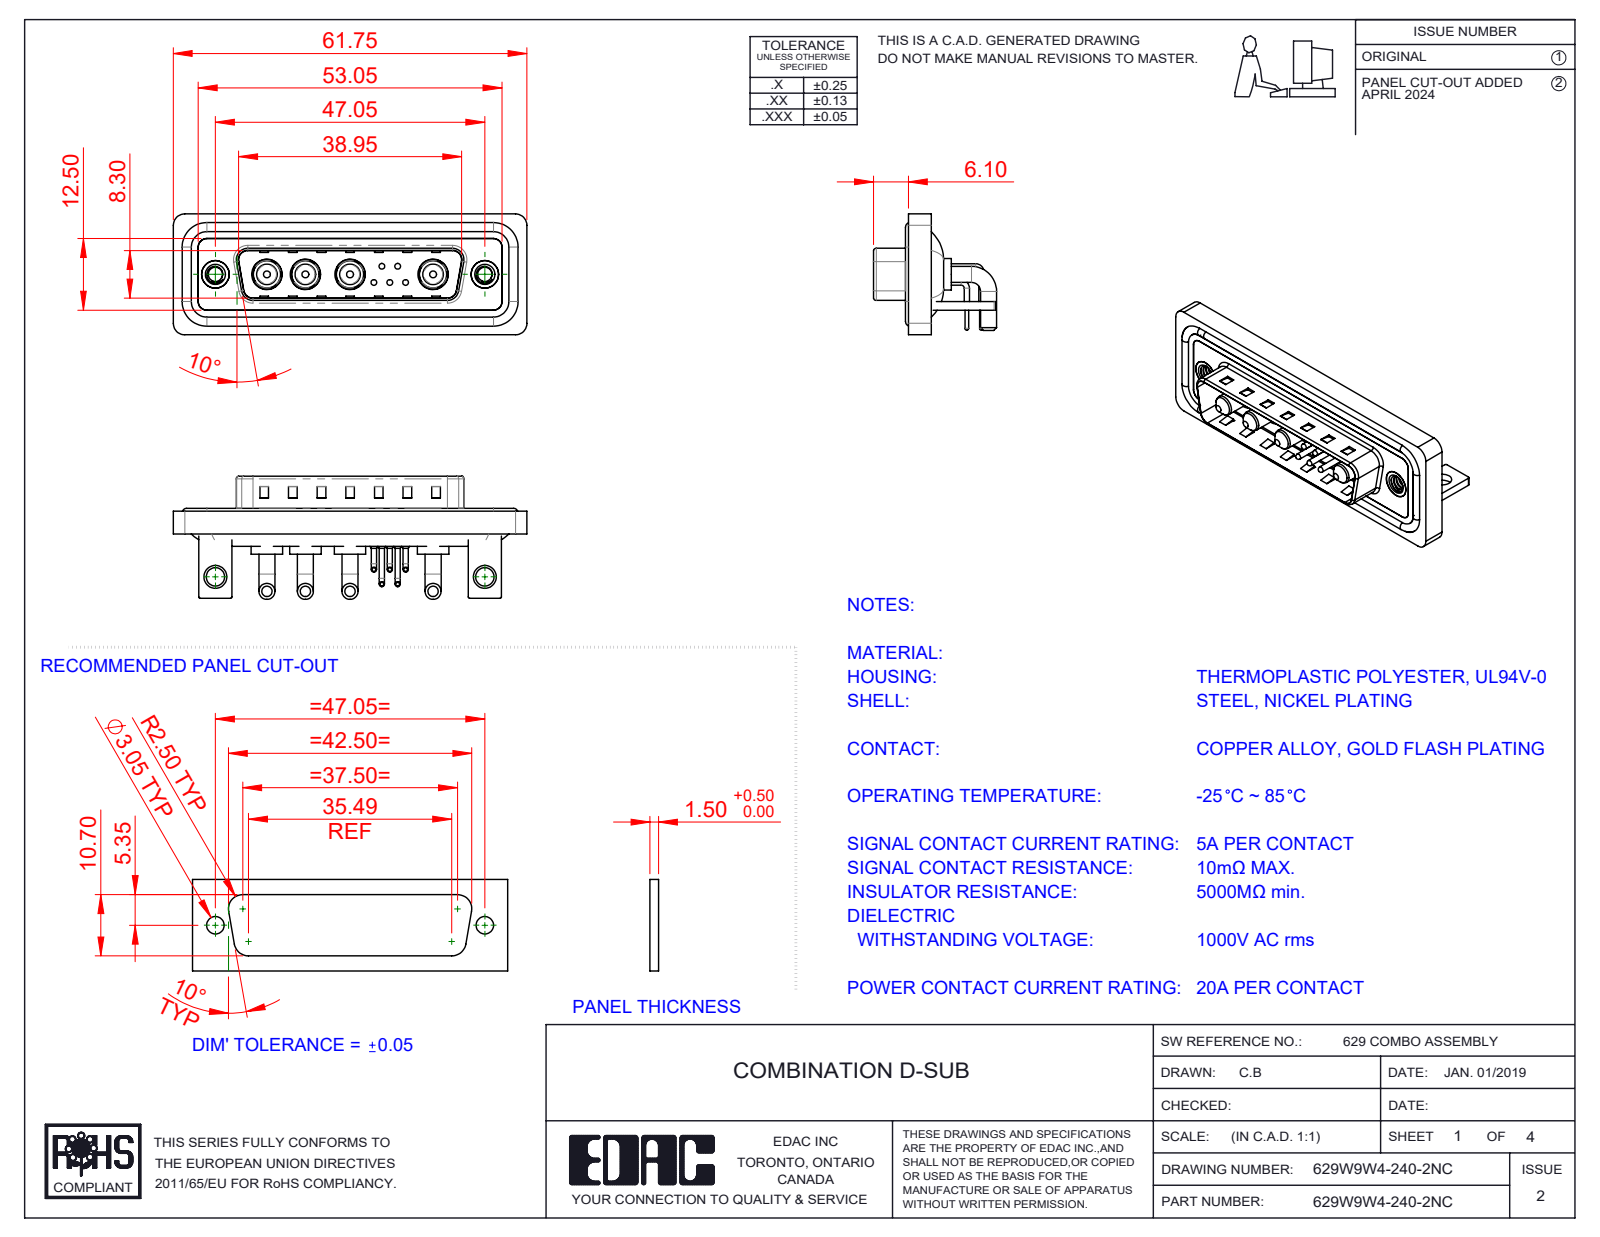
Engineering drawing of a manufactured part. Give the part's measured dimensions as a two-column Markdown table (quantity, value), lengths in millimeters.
| quantity | value |
| --- | --- |
| part name | 629Combo Shell Front_25 Contacts; 629Combo Housing_9W4; 629Combo Waterproof Housing_25 Contacts; 629Combo Contact Row 1 (+6 more) |
| STEP written by | SolidWorks 2023 (CONFIG_CONTROL_DESIGN) |
| units | millimeters |
| bodies | 22 solids, 1243 faces (589 planar, 470 cylindrical, 184 other) |
| overall size | 61.75 × 21.5 × 21.1 |
| volume | 7 976 mm³ |
| surface area | 12 964 mm² |
| round holes (diameter × count) | 0.75 × 5, 1.6 × 5, 2 × 5, 4.85 × 4, 5.3 × 4, 2.5 × 2, 3.2 × 2, 4 × 2, 4.8 × 2, 5 × 2 |
| round bosses / shafts (diameter × count) | 0.9 × 10, 2.8 × 8, 1.5 × 5, 1 × 5, 0.65 × 5, 5.5 × 4, 5.2 × 4, 4.75 × 4 |
| partial cylindrical surfaces (radius × count) | 2 × 19, 1.5 × 18, 0.25 × 16, 0.5 × 9, 1.6 × 8, 1.01 × 5, 0.6 × 4, 0.65 × 4 |
| main face-to-face distances | 0.4, 1.5, 0.8, 2.9, 2.1, 1.1, 3.7, 4.1, 4.5, 1.6 |
| hole center spacings | 3.16, 2.77, 5.04, 14.5, 47.05, 2.78, 4.4, 4.41 |
